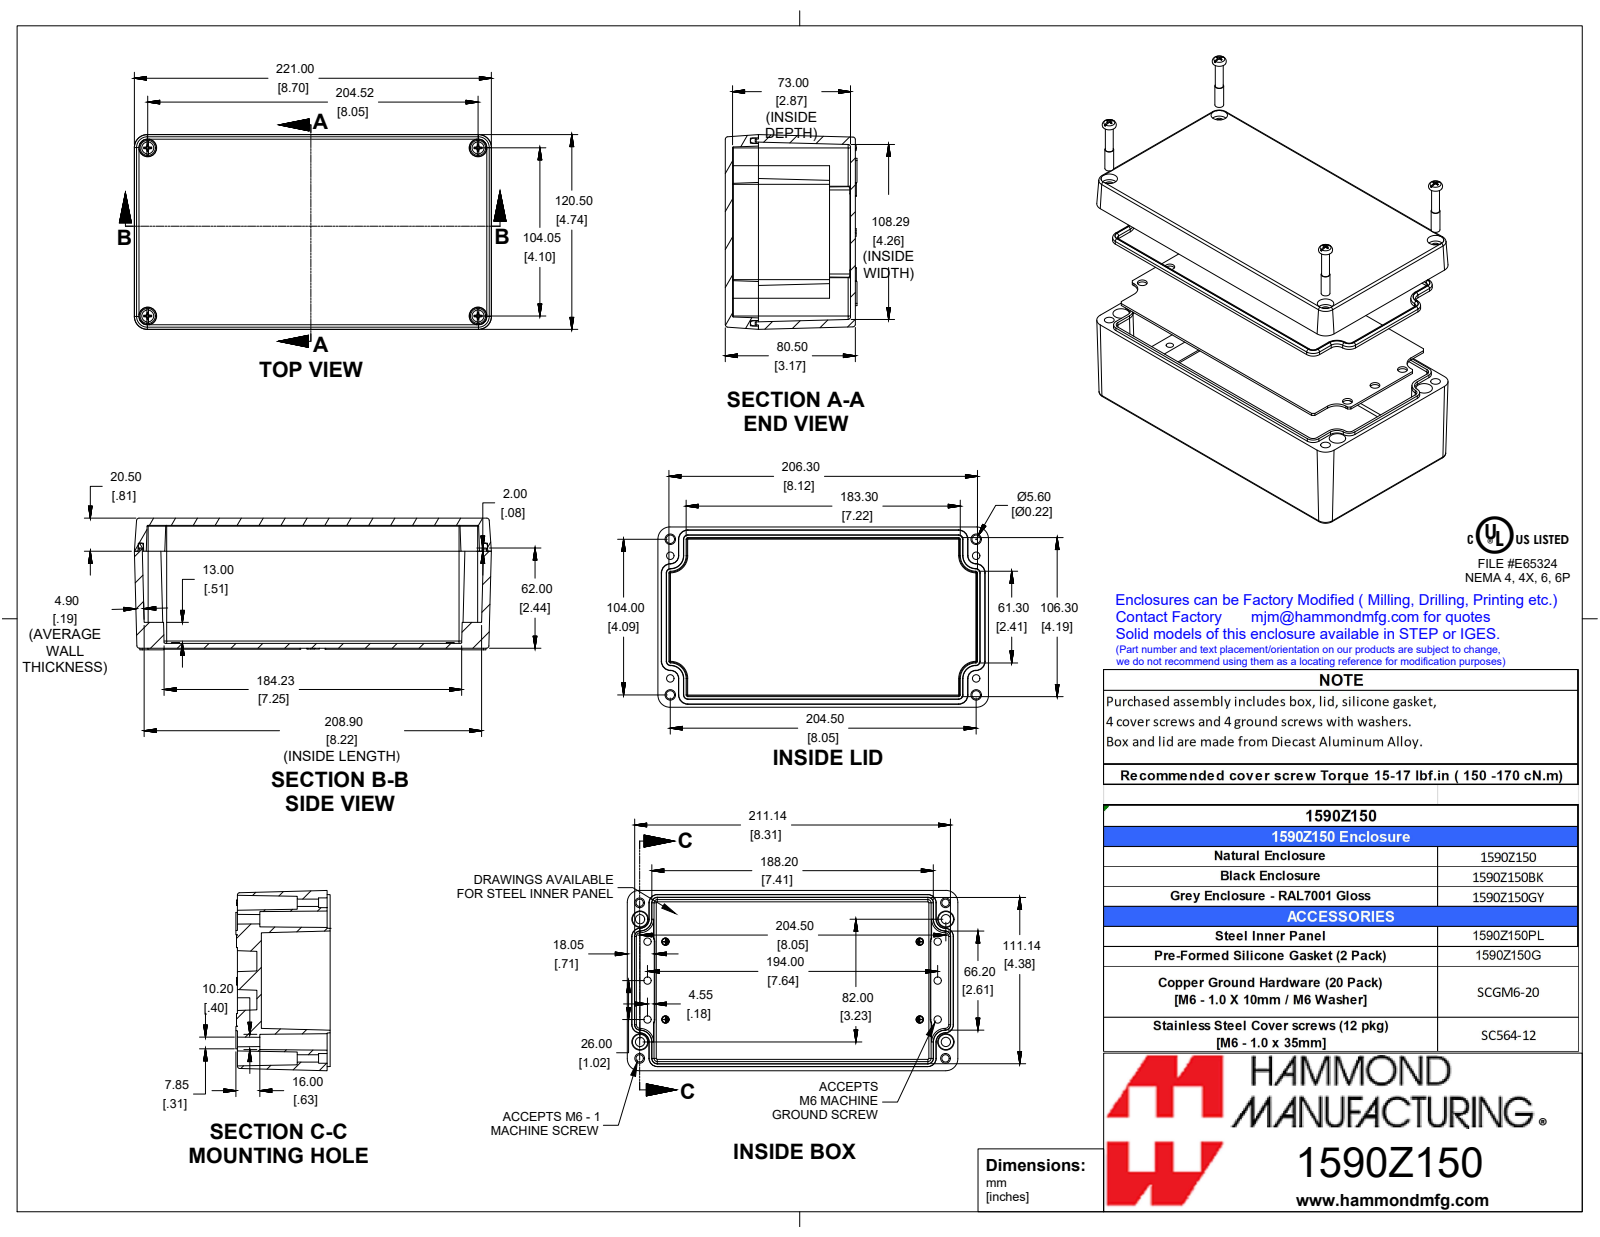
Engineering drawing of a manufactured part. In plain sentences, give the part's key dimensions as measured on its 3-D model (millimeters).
The part is named "1590Z150BK". Its 3-D file was written by "SolidWorks 2019 (CONFIG_CONTROL_DESIGN)". It is 8 solids with 762 faces: 404 planar, 80 cylindrical and 278 other. Overall it measures 221 by 120.5 by 81.5 millimeters. Its volume is 522 700 cubic millimeters and its surface area 280 800 square millimeters. Round holes: 10 of diameter 4.9, 6 of diameter 6.5, 4 of diameter 5, 4 of diameter 5.6, 4 of diameter 6.5, 4 of diameter 7. Round bosses or shafts: 4 of diameter 5.9, 4 of diameter 5.3. Partial cylindrical surfaces (rounded edges, fillets, slot ends): 24 of radius 1.5, 6 of radius 0.5, 4 of radius 8.6. The main face-to-face distances are 80.5, 3, 76, 4.5, 18, 58, 62.5, 16.4, 1.6, 59.6. The hole center spacings are 194, 199.8, 200.8, 200.9, 11, 15.9, 15.9, 26.
